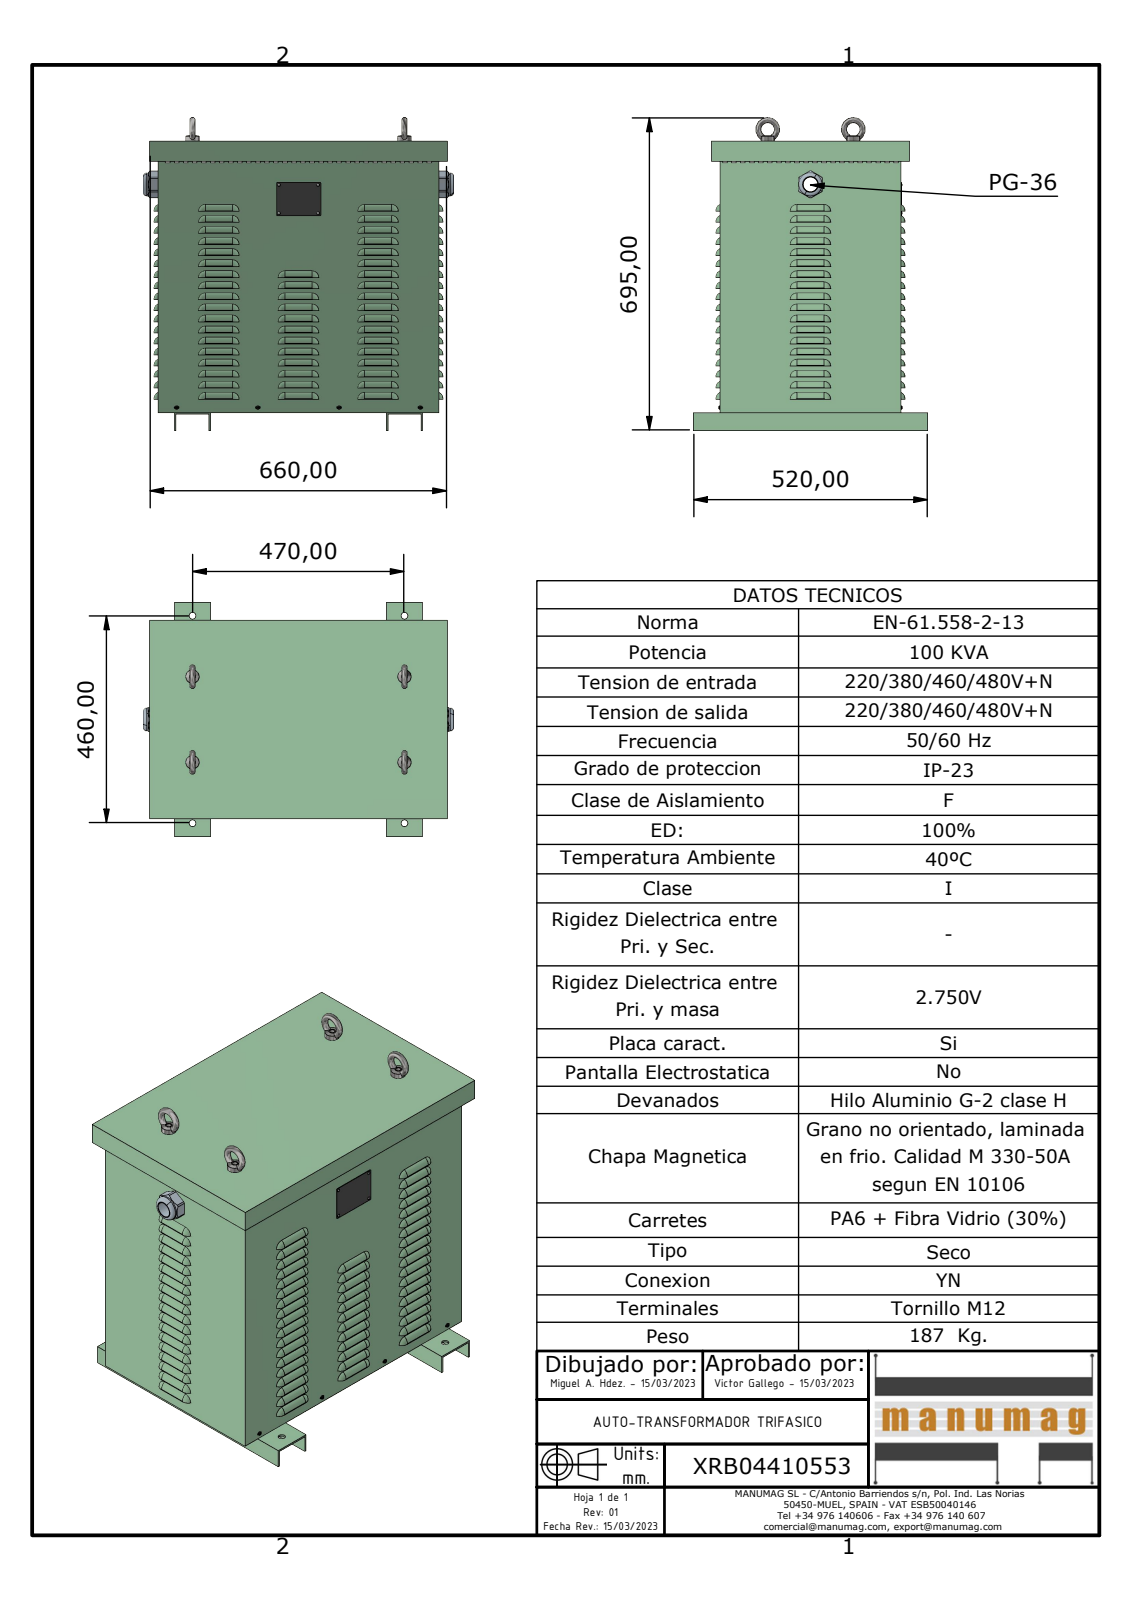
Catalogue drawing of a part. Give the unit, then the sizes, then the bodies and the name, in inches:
Units: inches
Overall size (bounding box): 27.362 × 27.094 × 20.472
Round holes (diameter × count): ⌀0.433 ×558, ⌀0.591 ×8, ⌀0.157 ×4, ⌀0.197 ×4, ⌀0.398 ×4, ⌀1.26 ×1, ⌀1.89 ×1
Round bosses / shafts (diameter × count): ⌀1.181 ×4, ⌀0.157 ×4, ⌀0.143 ×4, ⌀0.126 ×4, ⌀2.012 ×2, ⌀1.868 ×1, ⌀1.85 ×1
Partial cylindrical surfaces — rounded edges, fillets, slot ends (radius × count): R0.551 ×132, R0.276 ×72, R0.591 ×72, R0.153 ×12, R0.098 ×8, R0.079 ×4, R1.181 ×2
Main face-to-face distances: 0.079, 15.748, 23.622, 24.449, 15.669, 15.827, 23.701, 24.37, 23.543, 24.528
Hole centre spacings: 1.181, 0.591, 22.913, 22.944, 7.835, 1.772, 22.921, 22.982
Volume: 297.8 in³ · Surface area: 6 654 in²
Bodies: 24 solids, 3065 faces (1141 planar, 1208 cylindrical, 716 other)
Part name (STEP PRODUCT): XRB04410553; JE100 CUERPO; JE100 BASE; PLACA CARACTERISTICAS (+6 more)
STEP written by: Autodesk Inventor 2023 (AUTOMOTIVE_DESIGN)
